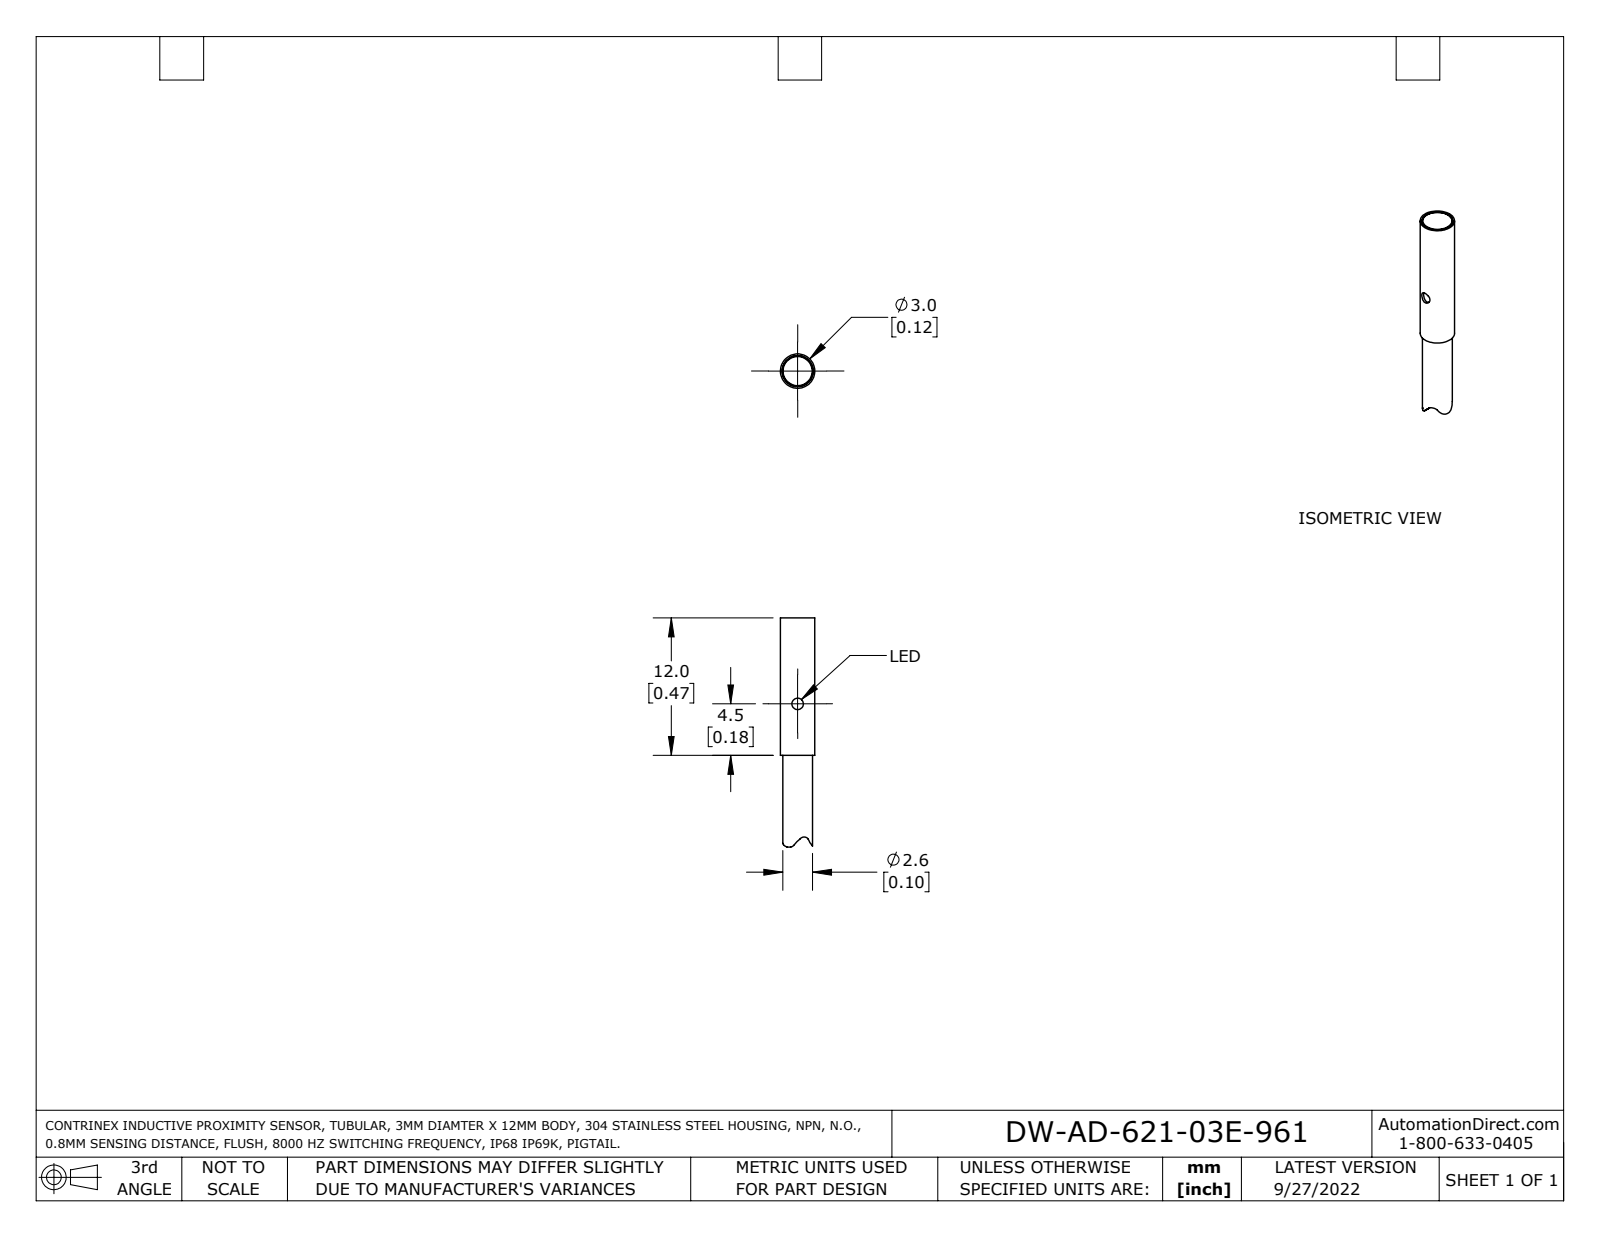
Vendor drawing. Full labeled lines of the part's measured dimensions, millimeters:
Part name (STEP PRODUCT): DW-AD-621-03E-961
STEP written by: SolidWorks 2021 (AUTOMOTIVE_DESIGN)
Units: millimetres
Bodies: 1 solid, 21 faces (6 planar, 13 cylindrical, 2 other)
Overall size (bounding box): 20 × 3 × 3
Volume: 100 mm³ · Surface area: 210 mm²
Round holes (diameter × count): ⌀1 ×1, ⌀2.7 ×1
Round bosses / shafts (diameter × count): ⌀3 ×1, ⌀2.6 ×1, ⌀2.6 ×1
Partial cylindrical surfaces — rounded edges, fillets, slot ends (radius × count): R0.4 ×1, R0.6 ×1, R2.4 ×1, R3.6 ×1, R4.8 ×1
Main face-to-face distances: 12, 20, 8, 11, 1, 9, 10.9, 11.9, 19.9
